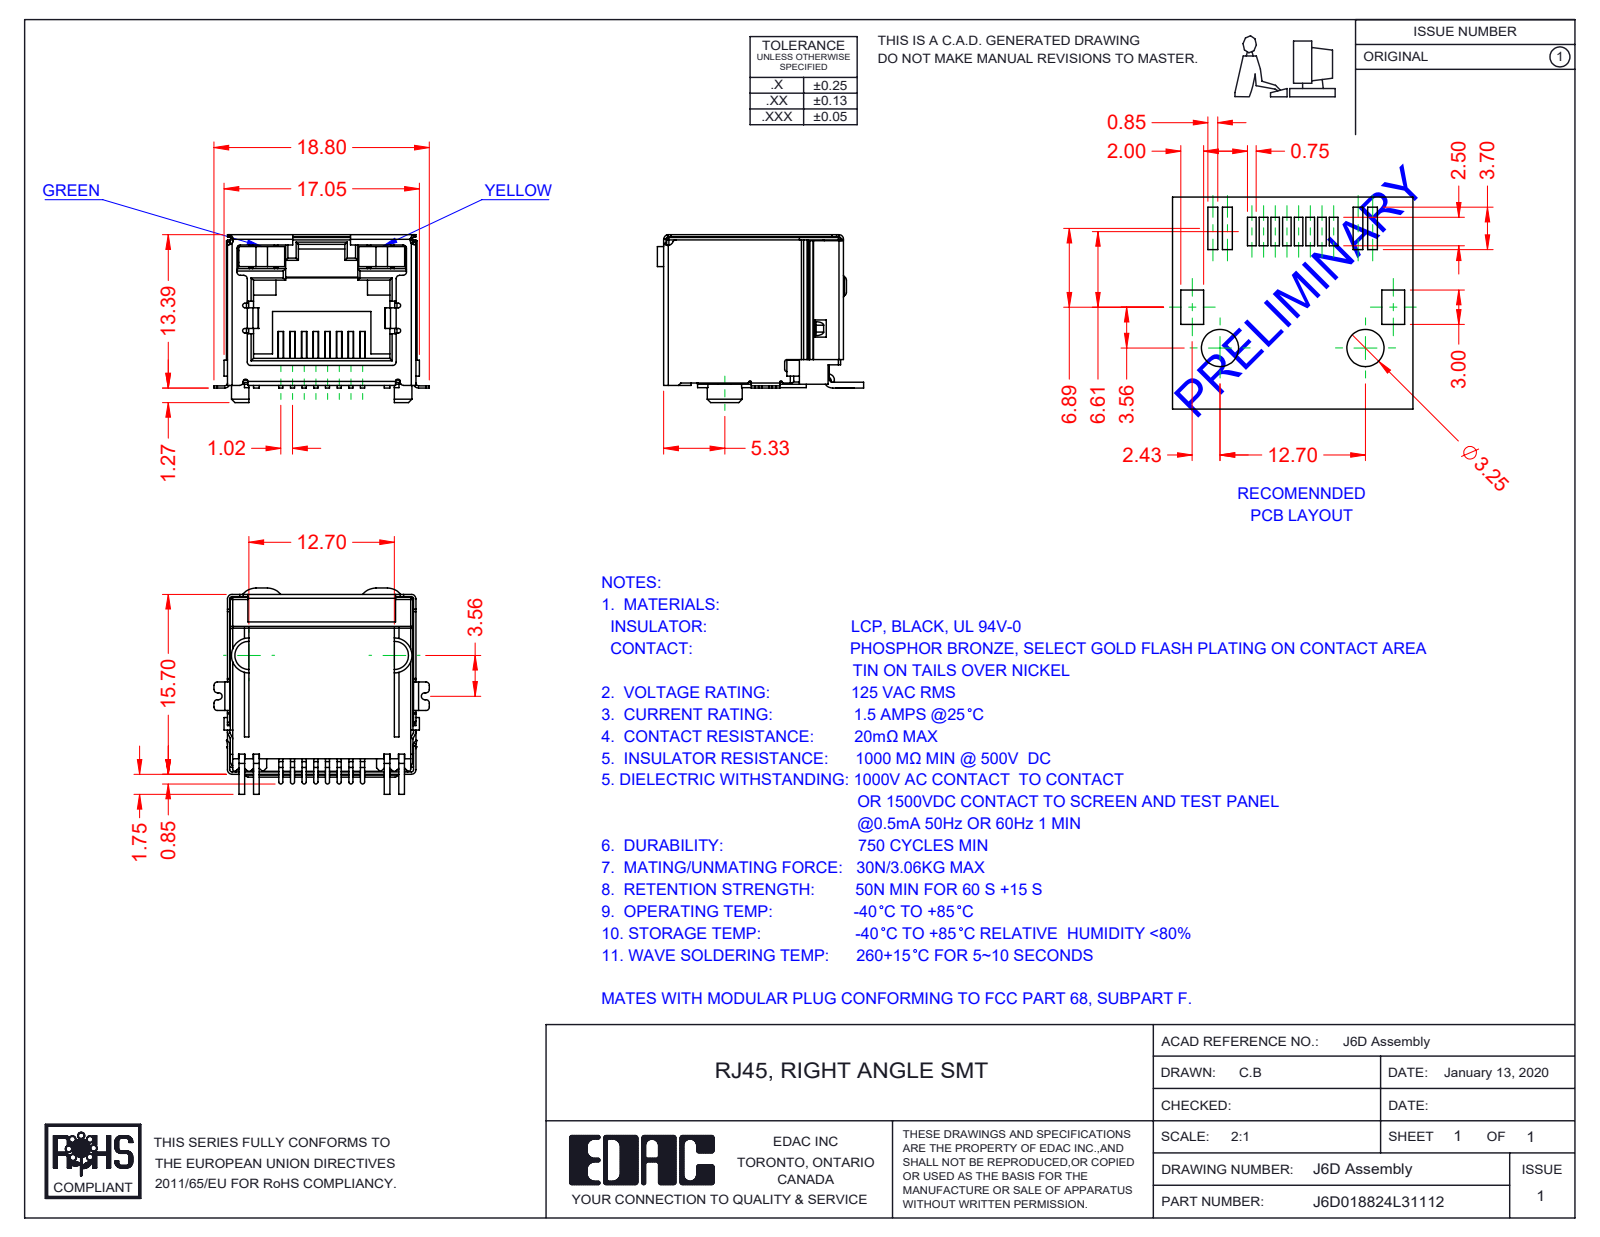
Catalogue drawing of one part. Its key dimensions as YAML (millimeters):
part_name: "J6D018824L31112; 6D Shield_LED - No EMI; 6D LED LH_3-Green; 6D Contacts (+2 more)"
step_written_by: "SolidWorks 2016 (CONFIG_CONTROL_DESIGN)"
units: millimeters
bodies: {solids: 12, faces: 893, planar: 644, cylindrical: 216, other: 33}
overall_size: [18.8, 18, 14.65]
volume: 1804
surface_area: 4898
partial_cylinders:
  - {radius: 0.3, count: 39}
  - {radius: 0.2, count: 37}
  - {radius: 0.4, count: 16}
  - {radius: 0.1, count: 12}
  - {radius: 0.15, count: 8}
  - {radius: 0.18, count: 8}
  - {radius: 0.5, count: 6}
  - {radius: 1.5, count: 5}
face_to_face_distances: [16, 16.25, 16.2, 2.25, 1, 15.95, 16.05, 12.8, 0.45, 16.45]
